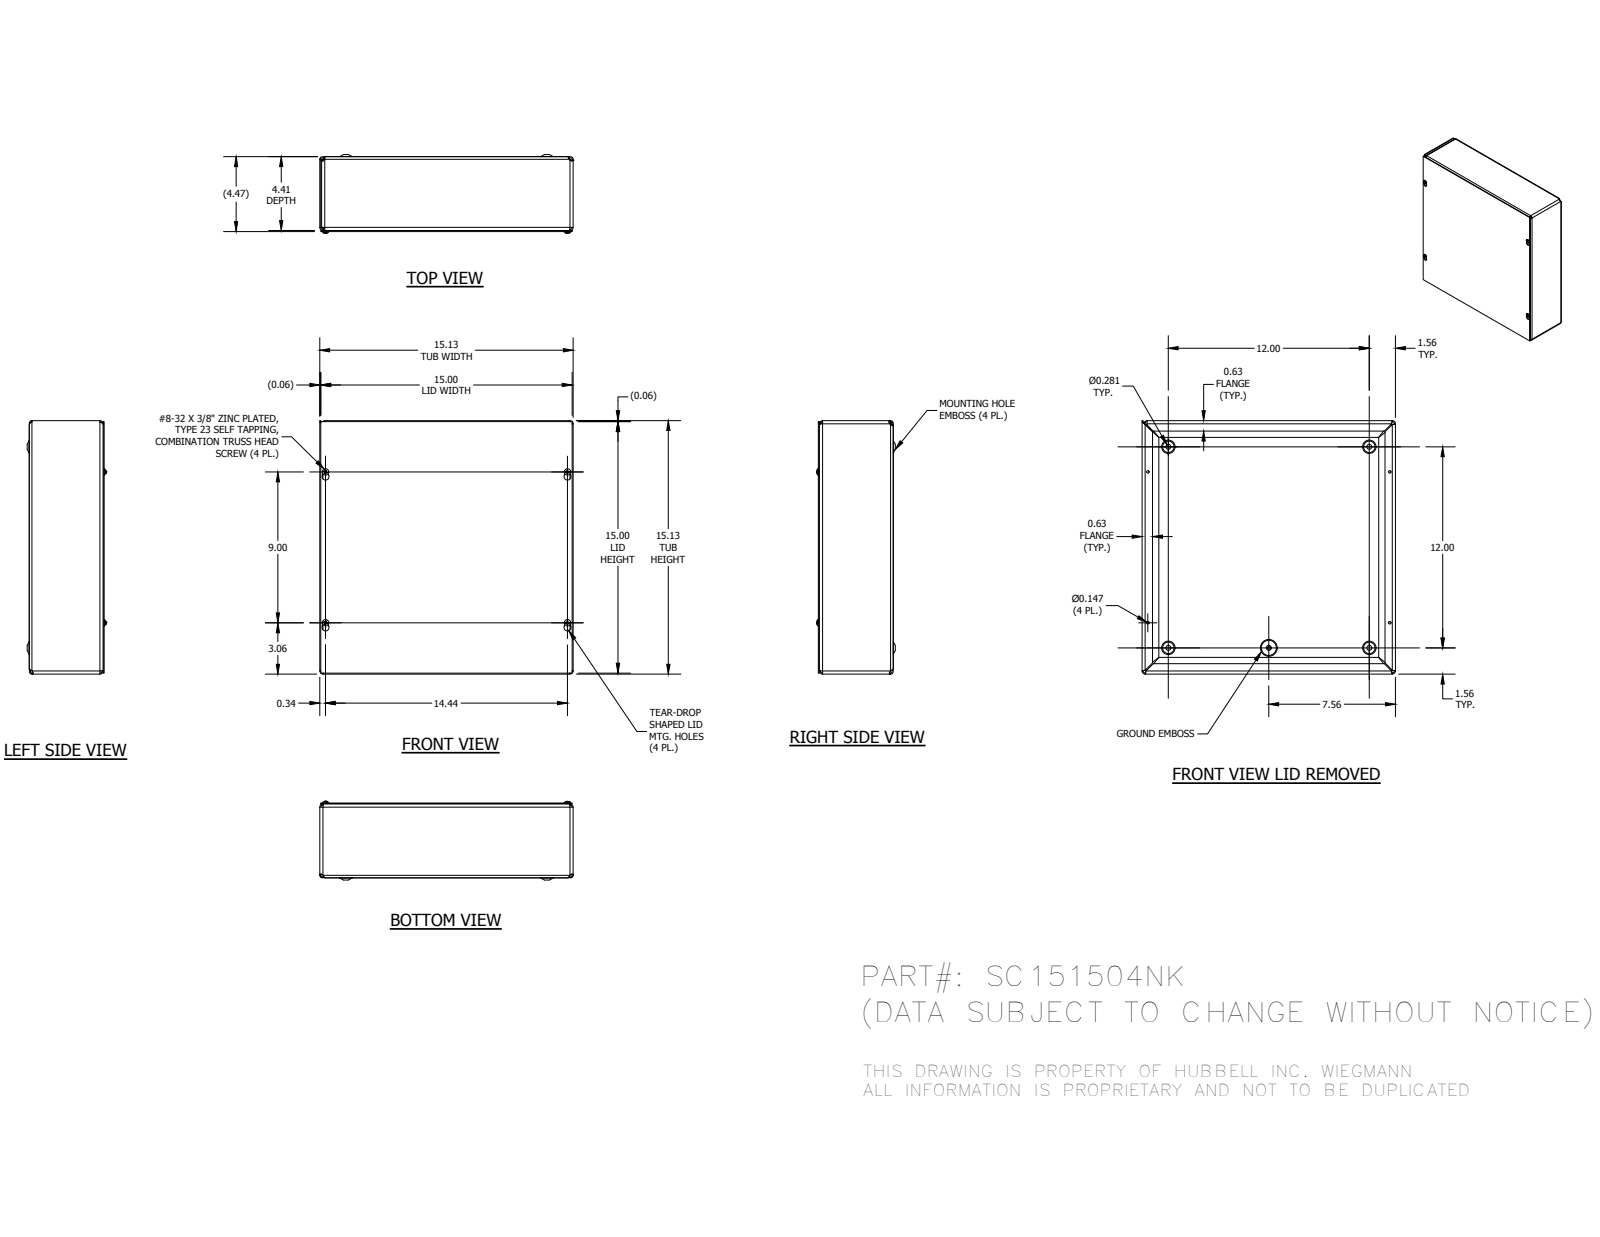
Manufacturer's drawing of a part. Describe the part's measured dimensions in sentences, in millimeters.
The part is named "SC1515BKP; SC151504NKWRA; SC1515LID; 34056 (+1 more)". Its 3-D file was written by "Autodesk Inventor 2014 (AUTOMOTIVE_DESIGN)". It is 7 solids with 357 faces: 132 planar, 67 cylindrical and 158 other. Overall it measures 384.18 by 384.18 by 119.2 millimeters. Its volume is 798 340 cubic millimeters and its surface area 1 023 000 square millimeters. Round holes: 4 of diameter 3.73, 4 of diameter 7.62, 1 of diameter 4.19. Round bosses or shafts: 4 of diameter 9.75, 4 of diameter 4.17, 1 of diameter 5.8. Partial cylindrical surfaces (rounded edges, fillets, slot ends): 12 of radius 3.17, 8 of radius 4.75, 4 of radius 1.4, 4 of radius 1.57, 4 of radius 2.38, 4 of radius 2.97, 4 of radius 3.15, 4 of radius 3.96. The main face-to-face distances are 1.57, 110.32, 382.6, 111.89, 1.59, 111.91, 113.48, 384.17, 381.03, 3.16. The hole center spacings are 49.09, 268.49, 304.8, 428.79, 152.4, 228.6, 323.65, 337.9.
